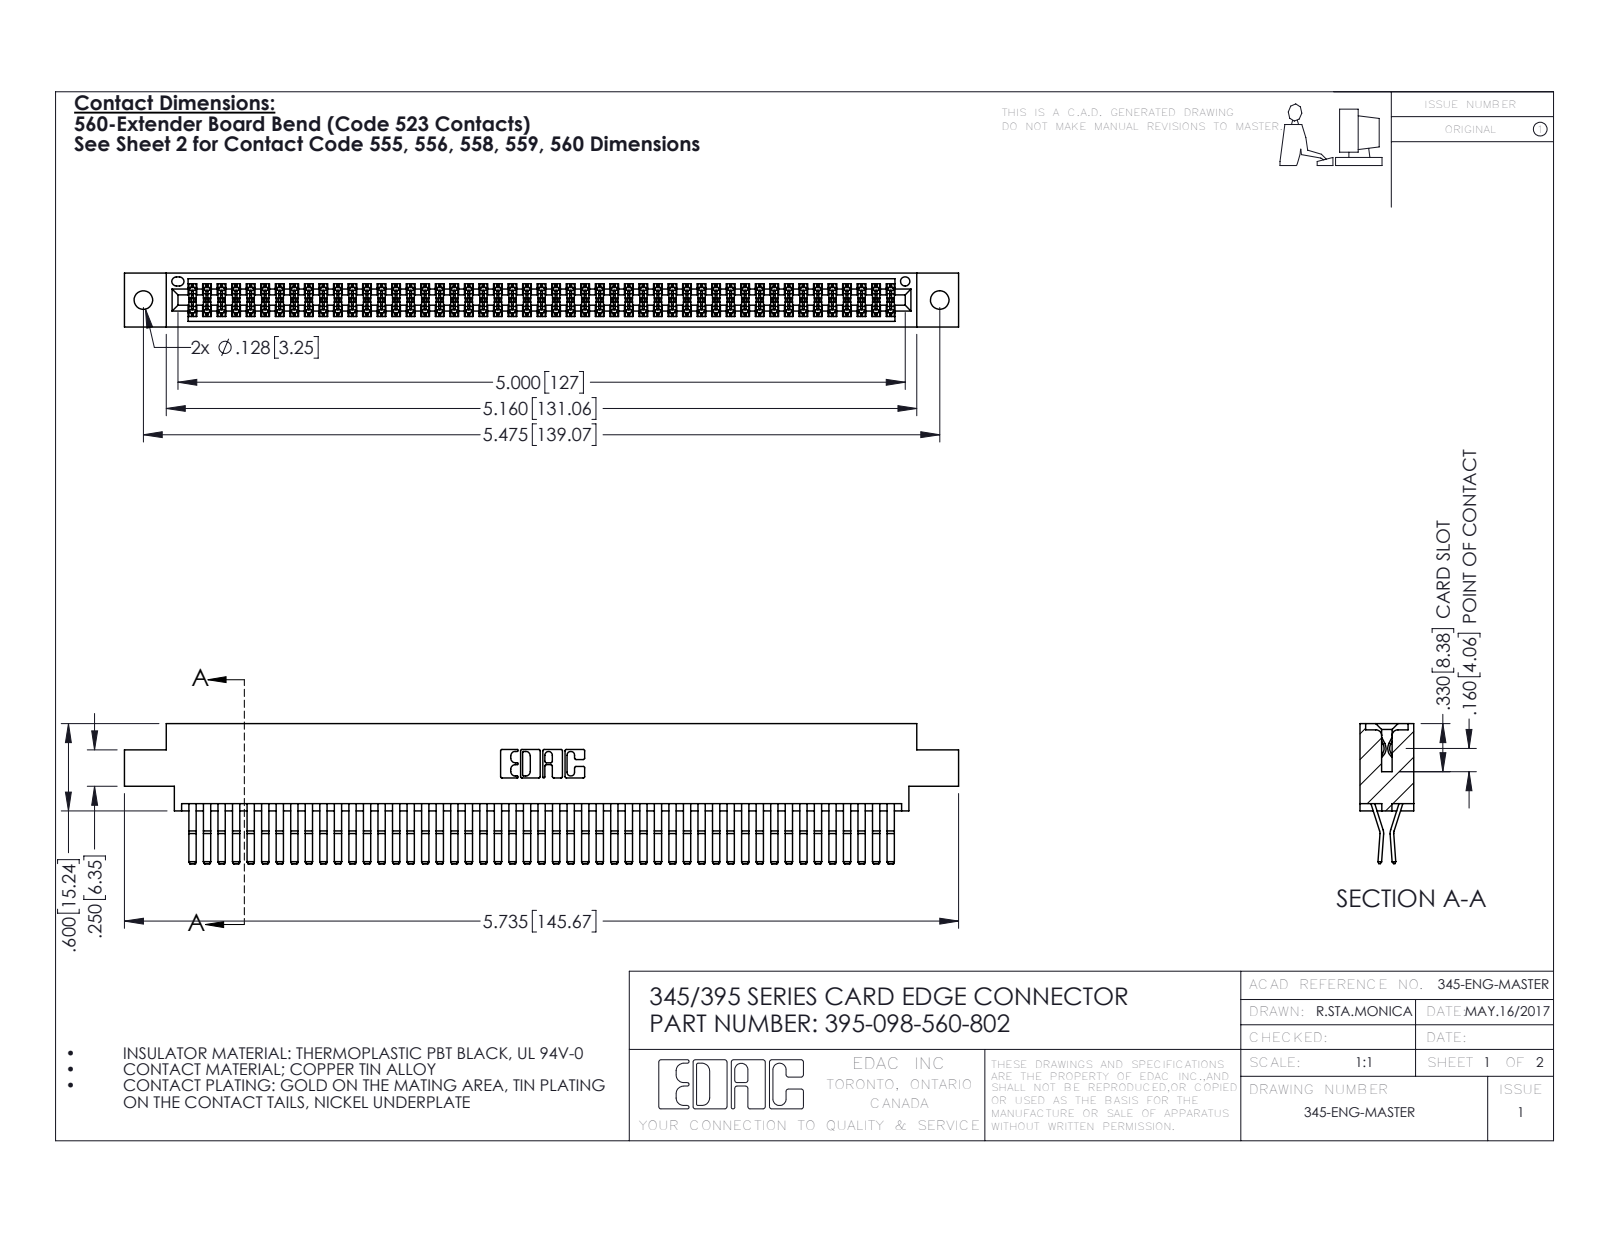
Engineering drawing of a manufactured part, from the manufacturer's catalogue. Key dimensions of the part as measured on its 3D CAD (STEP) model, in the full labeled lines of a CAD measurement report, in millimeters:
Part name (STEP PRODUCT): 345-292-001_560 Tail; 395-098-560-802; 345 Part_0.170 Offset - 0.128 Dia
STEP written by: SolidWorks 2016 (CONFIG_CONTROL_DESIGN)
Units: millimetres
Bodies: 99 solids, 5226 faces (3318 planar, 1908 cylindrical, 0 other)
Overall size (bounding box): 145.7 × 24.4 × 9.4
Volume: 14 700 mm³ · Surface area: 23 400 mm²
Round holes (diameter × count): ⌀3.3 ×2, ⌀1.6 ×1
Partial cylindrical surfaces — rounded edges, fillets, slot ends (radius × count): R0.2 ×147, R0.3 ×22, R0.2 ×6, R0.8 ×6, R0.7 ×3, R0.3 ×2, R0.4 ×2, R0.5 ×2
Main face-to-face distances: 0.6, 7.6, 1.8, 9.4, 5.1, 2.5, 6.9, 5.7, 4.4, 3.8
Hole centre spacings: 6.9, 133.1, 139.1
